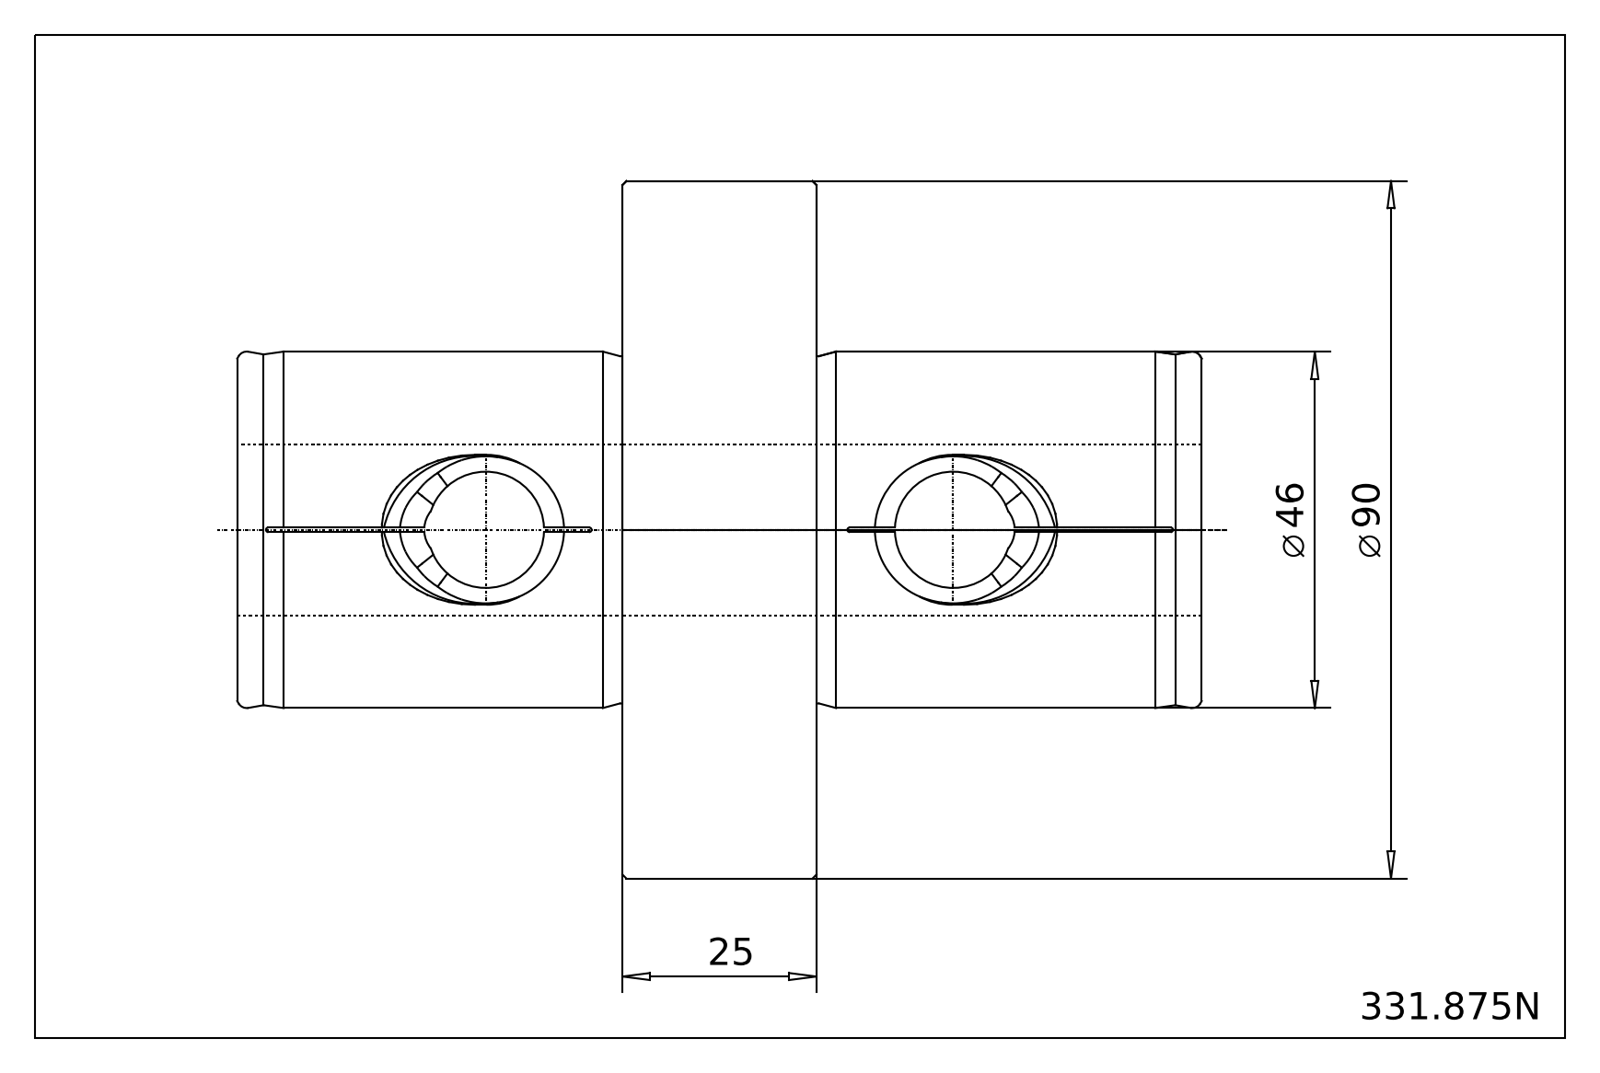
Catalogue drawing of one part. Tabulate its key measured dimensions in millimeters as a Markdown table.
| quantity | value |
| --- | --- |
| STEP written by | ACIS (automotive_design) |
| units | millimeters |
| bodies | 1 solid, 227 faces (83 planar, 22 cylindrical, 122 other) |
| overall size | 124.4 × 90 × 90 |
| volume | 262 643 mm³ |
| surface area | 42 928 mm² |
| round holes (diameter × count) | 13.5 × 6, 5 × 1, 22.1 × 1 |
| round bosses / shafts (diameter × count) | 90 × 1, 46 × 1 |
| main face-to-face distances | 25, 49.7, 74.7, 124.4, 124.39, 49.69, 74.69, 124.38, 2.18, 1.9 |
| hole center spacings | 63.1, 31.55 |
